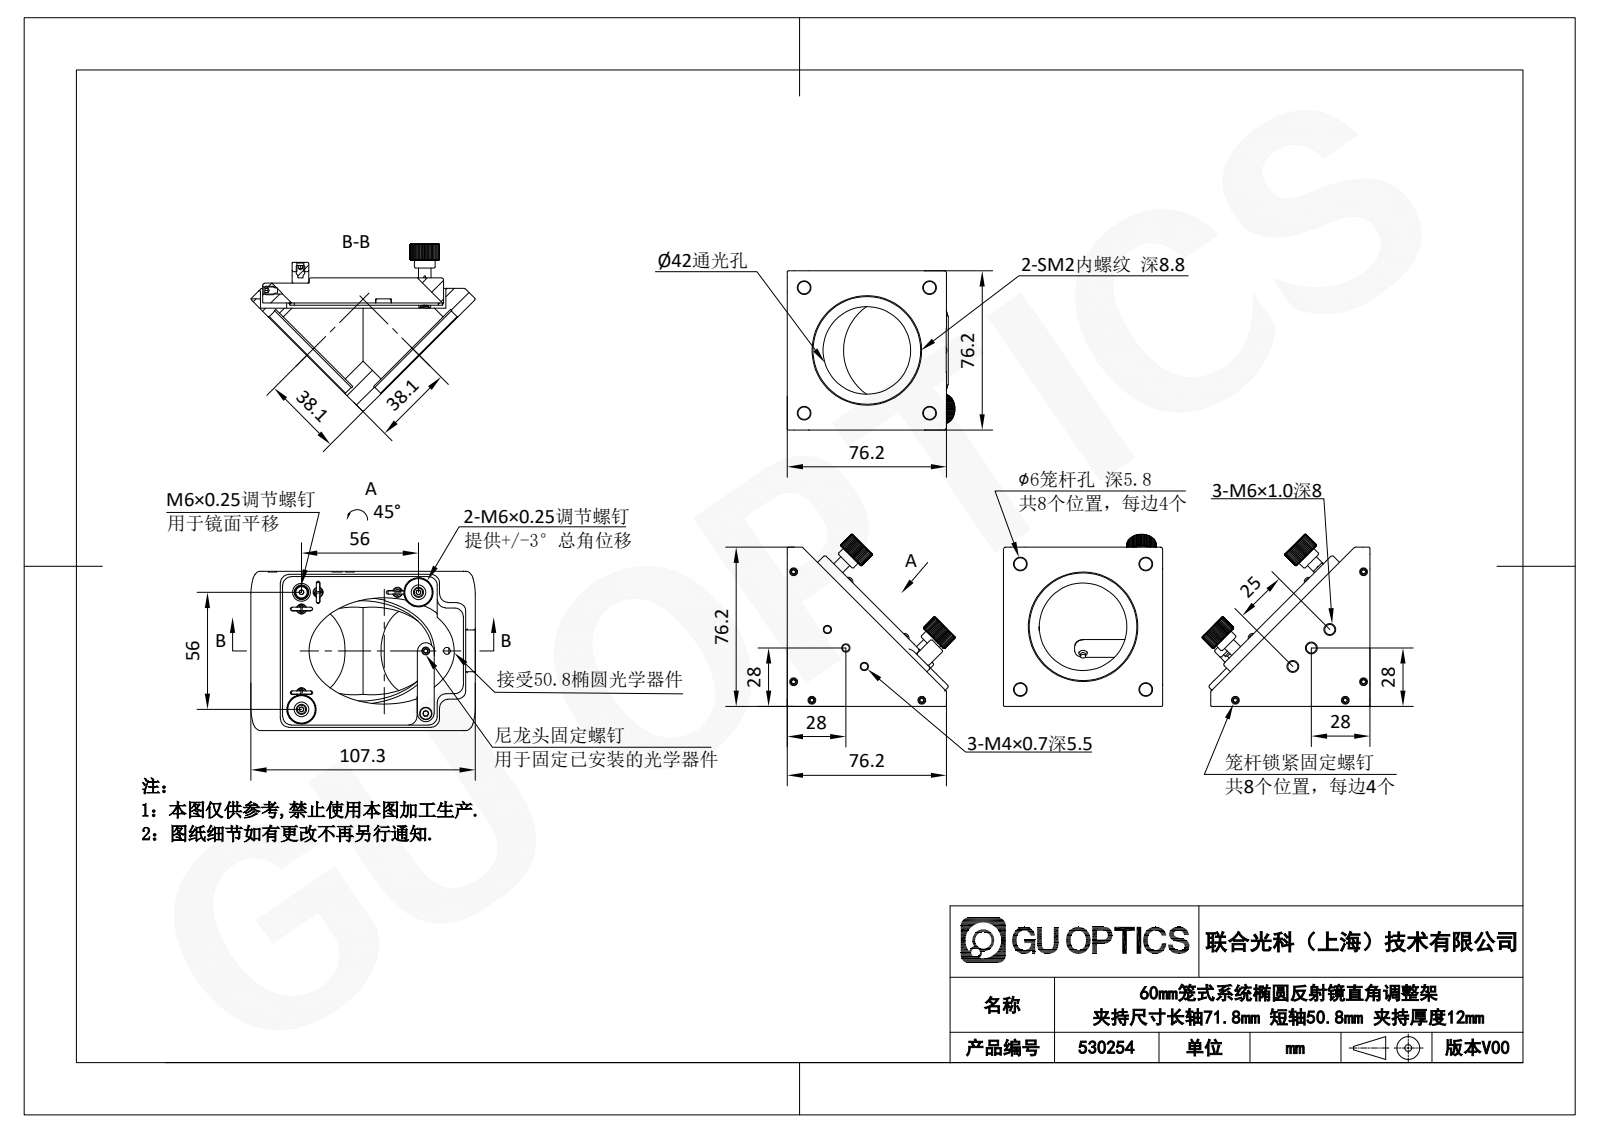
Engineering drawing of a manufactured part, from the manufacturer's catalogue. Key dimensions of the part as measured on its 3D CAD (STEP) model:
Part name (STEP PRODUCT): hexagon socket head cap screws gb_GB_FASTENER_SCREWS_HSHCS M3X10-N; hexagon socket head cap screws gb_GB_FASTENER_SCREWS_HSHCS M2X3-S; 3.03.31.14.042_RAMC-2BE-1-3_镜片安装配合板_ZA; GB／T79-2000内六角圆柱端紧定螺钉M4×6 (+4 more)
STEP written by: SolidWorks 2020 (CONFIG_CONTROL_DESIGN)
Units: millimetres
Bodies: 42 solids, 1381 faces (701 planar, 379 cylindrical, 301 other)
Overall size (bounding box): 82.36 × 80.23 × 76.2
Volume: 160 377 mm³ · Surface area: 60 364 mm²
Round holes (diameter × count): ⌀6 ×14, ⌀3.3 ×9, ⌀5 ×7, ⌀2.71 ×4, ⌀5.1 ×4, ⌀1.95 ×3, ⌀4.78 ×3, ⌀8.6 ×3, ⌀9.4 ×3, ⌀1.6 ×2, ⌀2.4 ×2, ⌀2.43 ×2
Round bosses / shafts (diameter × count): ⌀4 ×6, ⌀3.48 ×4, ⌀1.6 ×4, ⌀9.15 ×3, ⌀8.12 ×3, ⌀10 ×2, ⌀3.8 ×2, ⌀2.5 ×2
Partial cylindrical surfaces — rounded edges, fillets, slot ends (radius × count): R0.5 ×63, R4 ×19, R0.8 ×14, R0.9 ×8, R2 ×5, R3 ×4, R0.3 ×2, R7.1 ×2
Main face-to-face distances: 2.5, 76.2, 1.5, 5, 12, 13, 1, 1.1, 14.5, 9.5
Hole centre spacings: 48, 8, 42.43, 60, 56, 56.57, 19.98, 40
